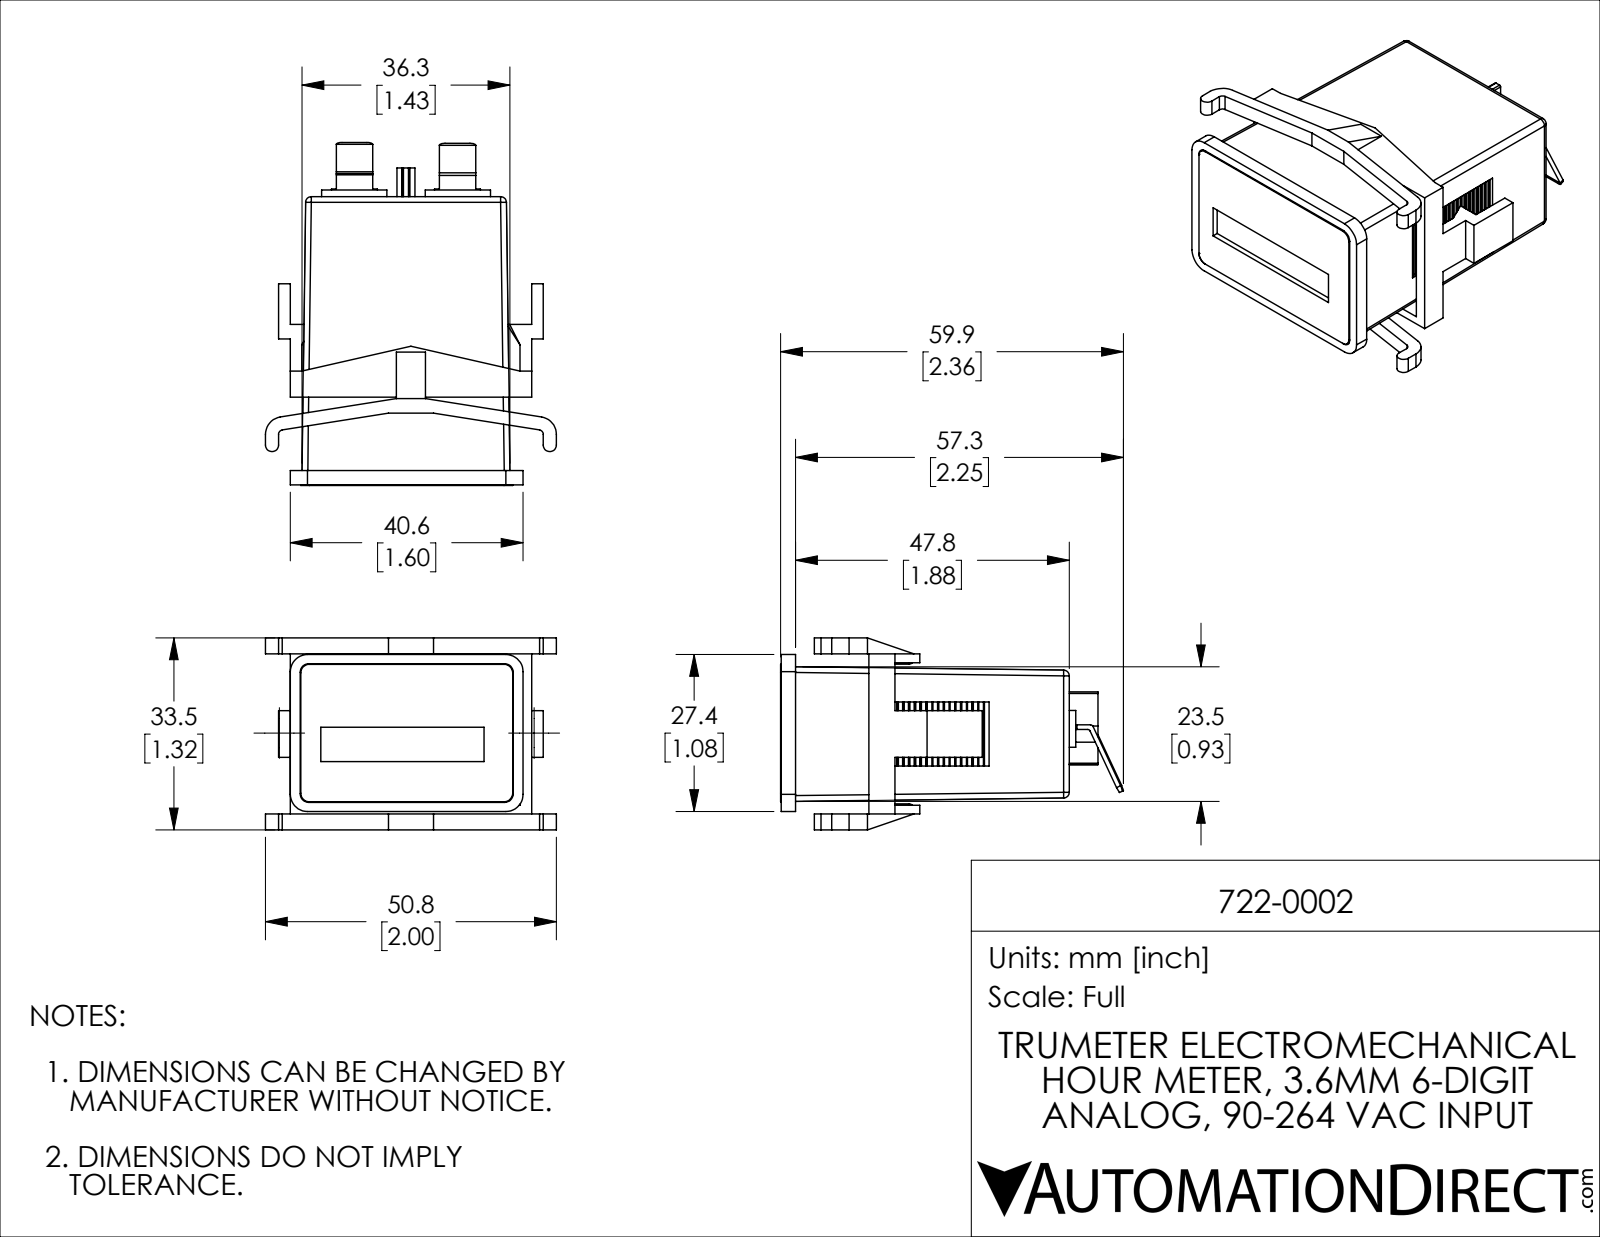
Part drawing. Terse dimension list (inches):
name: 722-0002
written by: SolidWorks 2021 (CONFIG_CONTROL_DESIGN)
unit: in
bodies: 5 solids, 564 faces (446 planar, 108 cylindrical, 10 other)
size: 2.357 × 2 × 1.32
volume: 0.827 in³; area: 32.02 in²
holes: 4× ⌀0.059
bosses: 1× ⌀0.039
rounds: 18× R0.02, 17× R0.039, 11× R0.012, 10× R0.059, 6× R0.035, 4× R0.01, 4× R0.014, 4× R0.118
face distances: 0.039, 0.08, 1.984, 1.945, 1.872, 0.073, 1.911, 1.66, 1.1, 0.063
hole spacings: 0.38, 0.411, 0.262, 0.747
